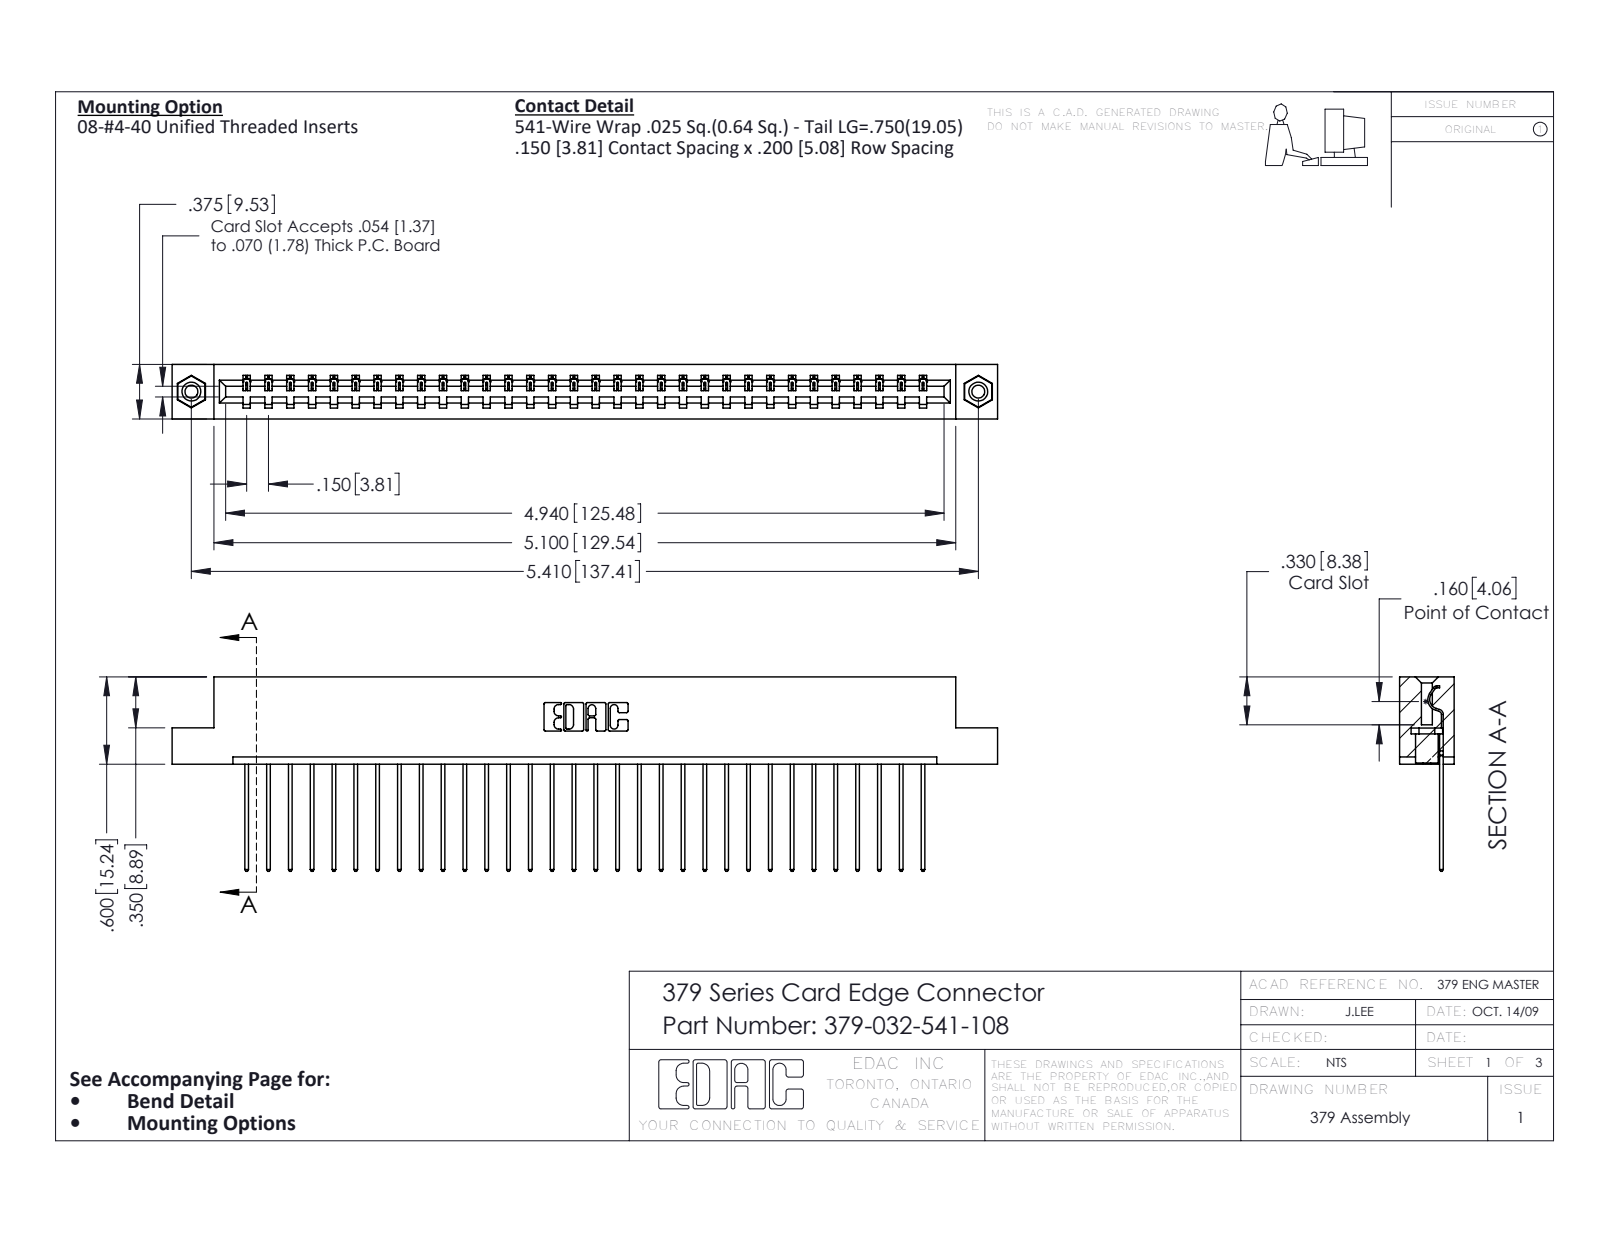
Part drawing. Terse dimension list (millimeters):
name: 379-032-541-108; 345-292-001_345-293-141; 379 Part_Flush - .156 Dia - TI; 345-250-001_345-250-003-102
written by: SolidWorks 2016 (CONFIG_CONTROL_DESIGN)
unit: mm
bodies: 35 solids, 2030 faces (1446 planar, 568 cylindrical, 16 other)
size: 144.1 × 34 × 9.5
volume: 15 100 mm³; area: 16 100 mm²
holes: 2× ⌀2.3, 2× ⌀3.2, 2× ⌀4
bosses: 2× ⌀3.9
rounds: 64× R0.2, 64× R0.3, 22× R0.3, 6× R0.2, 6× R0.8, 3× R0.7, 1× R0.4, 1× R0.6
face distances: 7.6, 1.9, 9.5, 5.7, 7, 2.5, 0.6, 5.1, 15.2, 14
hole spacings: 137.4
